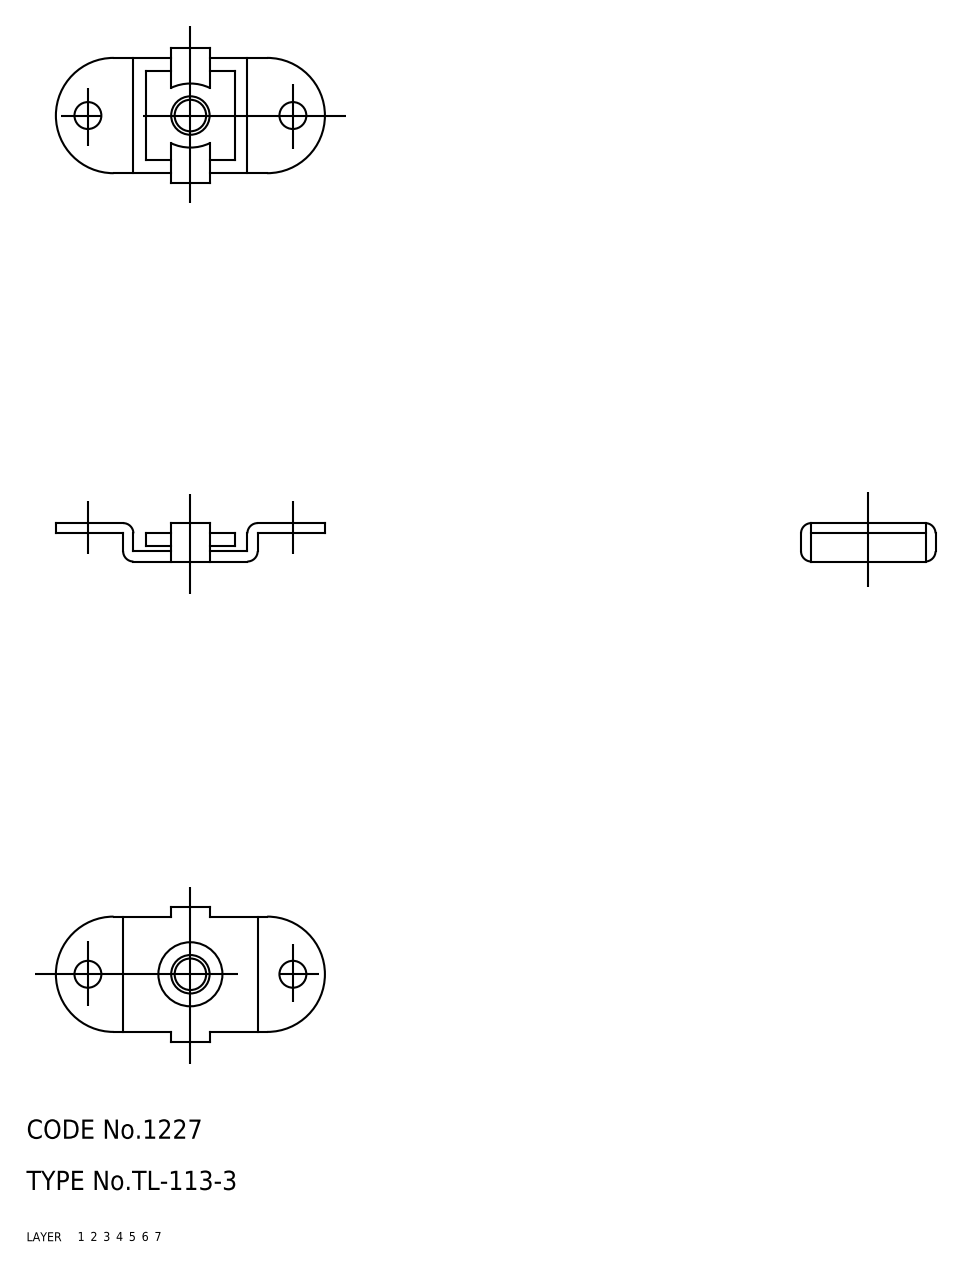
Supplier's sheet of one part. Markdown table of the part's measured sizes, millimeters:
| quantity | value |
| --- | --- |
| part name | 67111462; 67111475 |
| STEP written by | CADfix (AUTOMOTIVE_DESIGN) |
| units | millimeters |
| bodies | 2 solids, 52 faces (0 planar, 0 cylindrical, 52 other) |
| overall size | 42 × 21 × 6 |
| volume | 1 656 mm³ |
| surface area | 2 484 mm² |
